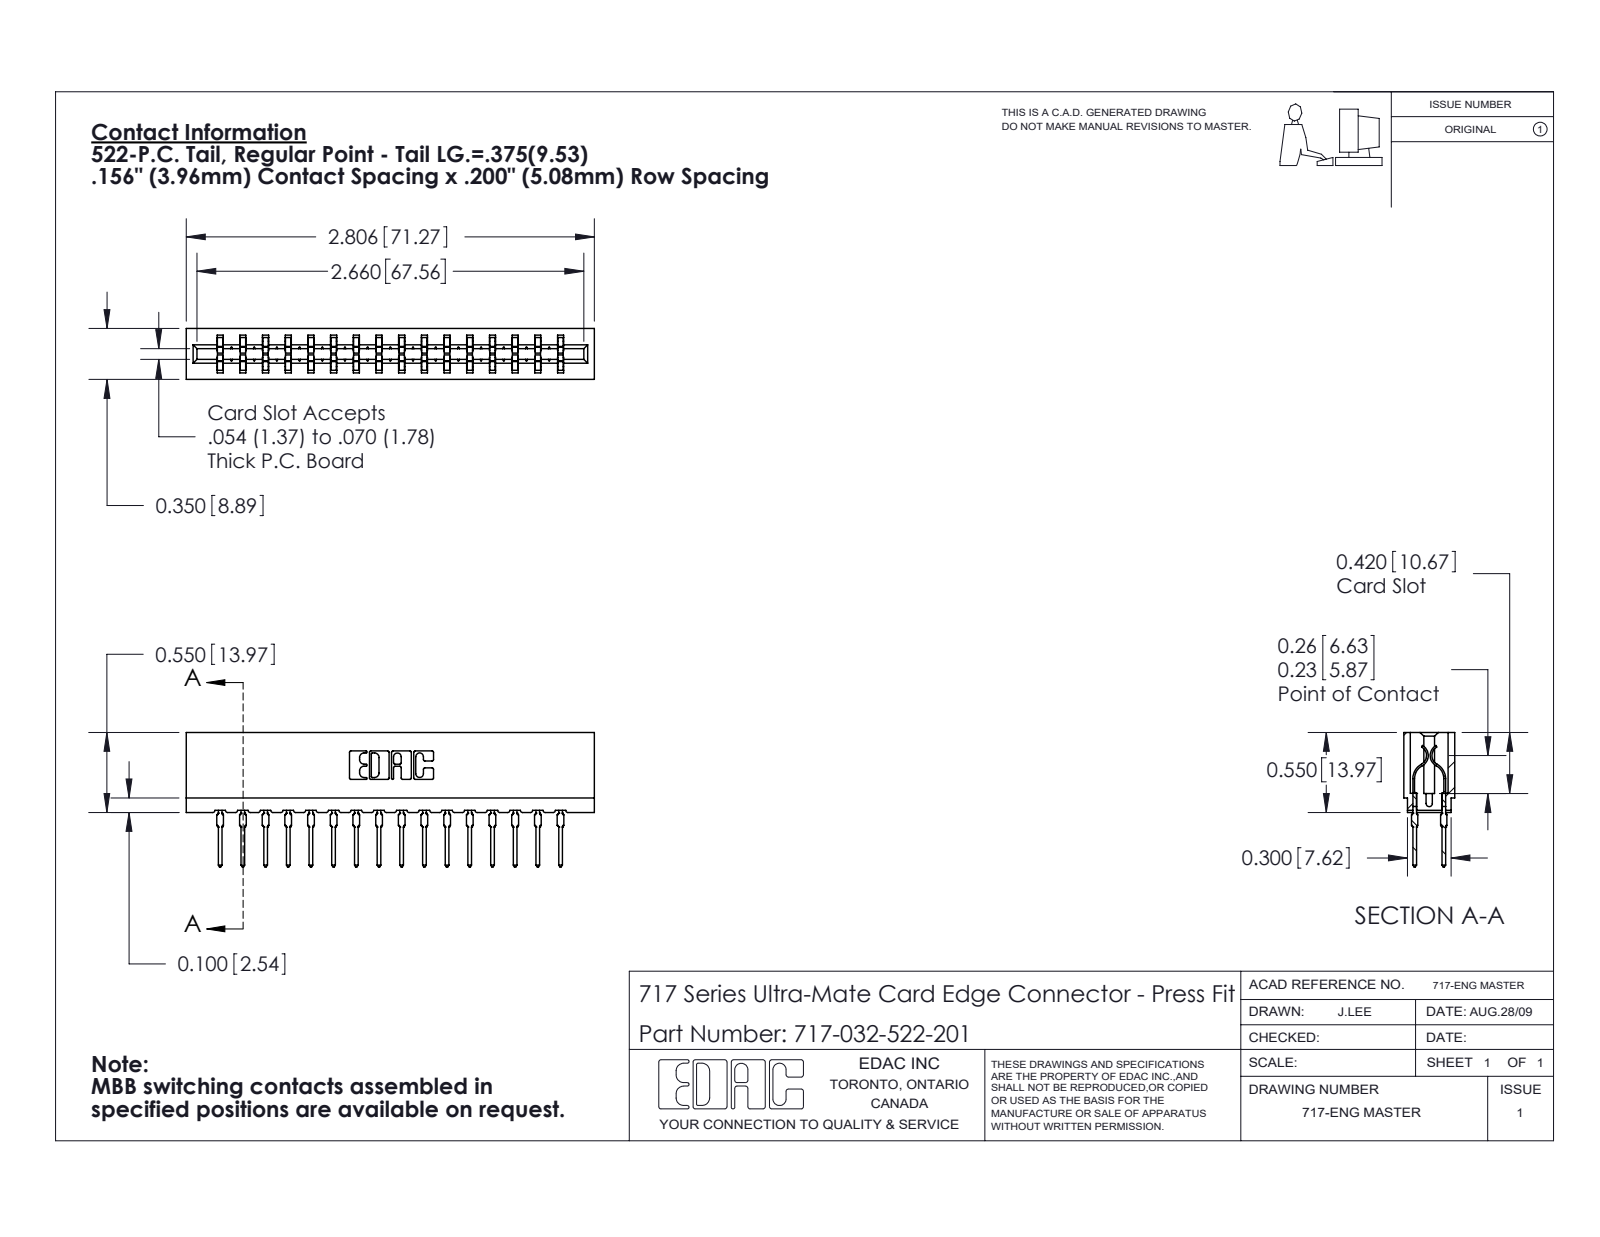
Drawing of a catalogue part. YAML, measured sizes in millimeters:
part_name: "717 Part_Insulator Option - 06; 717-032-522-201; 745-292-001_522"
step_written_by: "SolidWorks 2020 (CONFIG_CONTROL_DESIGN)"
units: millimeters
bodies: {solids: 33, faces: 2974, planar: 1542, cylindrical: 600, other: 832}
overall_size: [71.3, 23.5, 8.9]
volume: 6310
surface_area: 9439
partial_cylinders:
  - {radius: 0.5, count: 64}
  - {radius: 0.4, count: 32}
  - {radius: 0.3, count: 22}
  - {radius: 0.1, count: 8}
  - {radius: 0.3, count: 8}
  - {radius: 0.2, count: 6}
  - {radius: 0.8, count: 6}
  - {radius: 0.7, count: 3}
face_to_face_distances: [5.4, 3.5, 8.9, 4, 11.9, 15.8, 1.6, 7.3, 1.9, 3.8]
